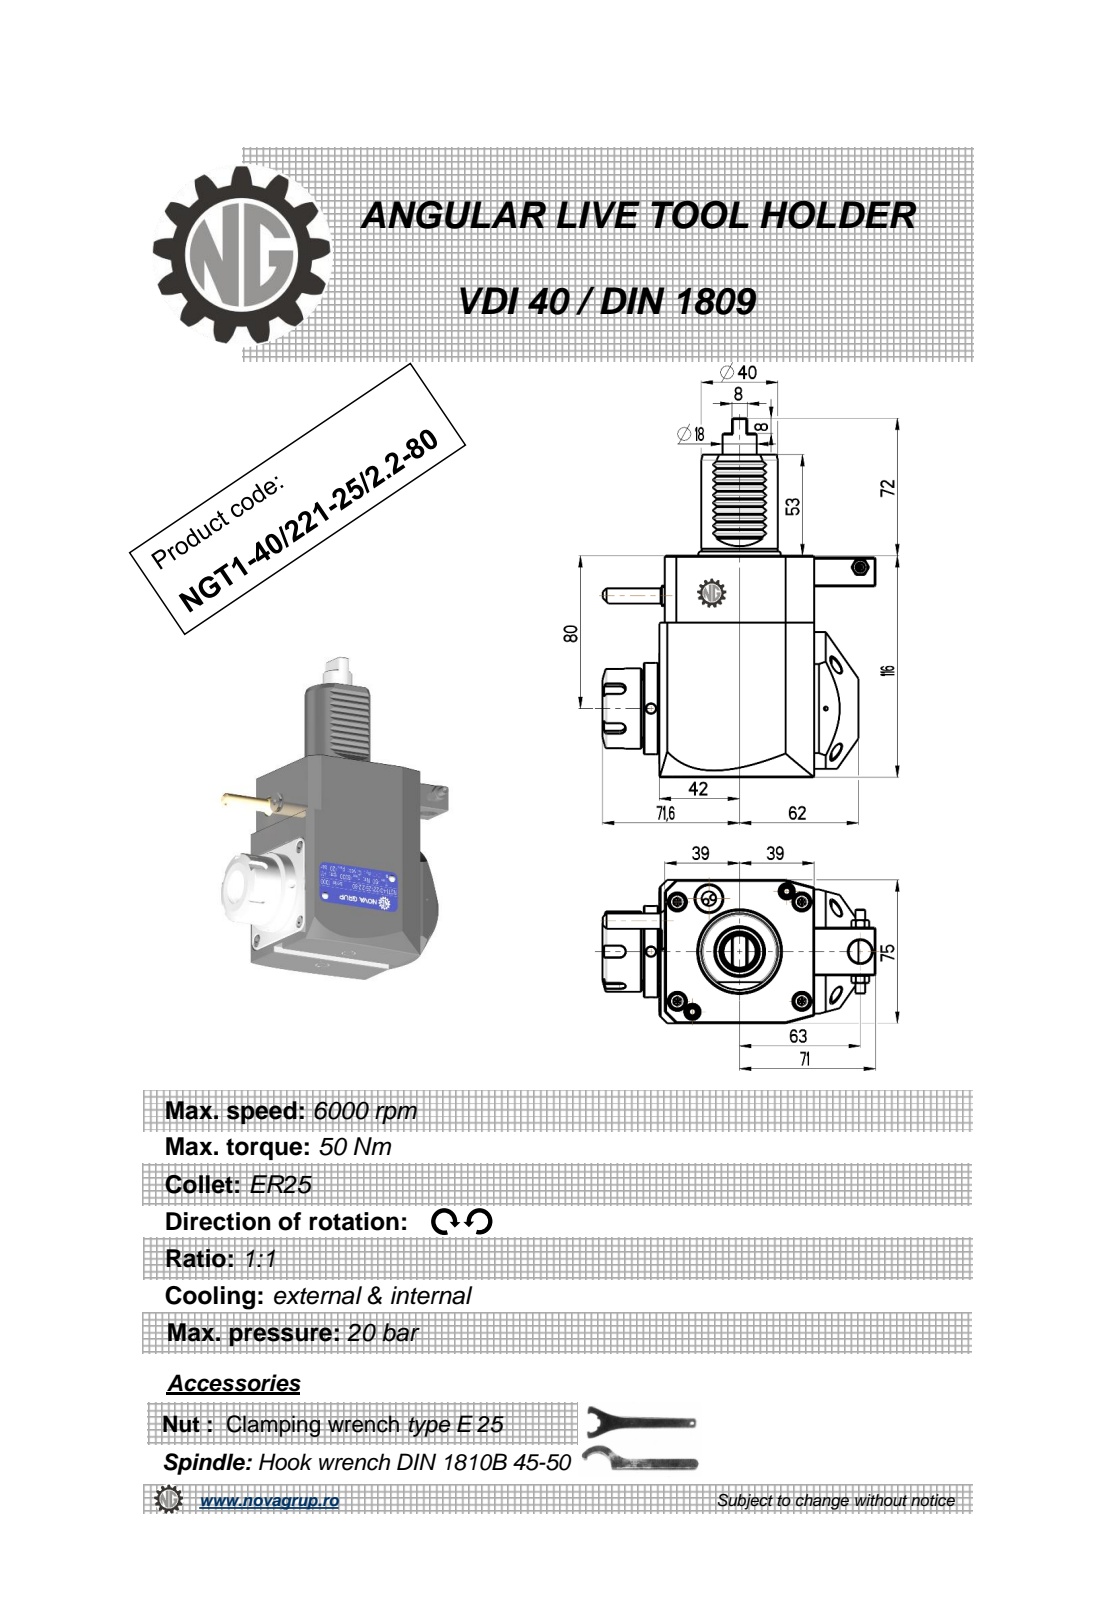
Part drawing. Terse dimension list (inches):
name: NGT1_40_221_25_2_2_80
written by: PRO/ENGINEER BY PARAMETRIC TECHNOLOGY CORPORATION, 2010280 (CONFIG_CONTROL_DESIGN)
unit: in
bodies: 1 solid, 432 faces (194 planar, 89 cylindrical, 149 other)
size: 7.402 × 5.614 × 3.016
volume: 52.89 in³; area: 108.2 in²
holes: 3× ⌀0.197, 1× ⌀0.118, 1× ⌀0.165, 1× ⌀0.374, 1× ⌀0.472, 1× ⌀0.799
bosses: 1× ⌀1.89, 1× ⌀1.654, 1× ⌀1.575, 1× ⌀1.476, 1× ⌀1.299, 1× ⌀0.701, 1× ⌀0.441, 1× ⌀0.353
rounds: 12× R0.01, 10× R0.012, 6× R0.009, 5× R0.118, 2× R0.031, 1× R0.02, 1× R1.575
face distances: 2.953, 4.567, 3.189, 0.118, 3.071, 0.11, 3.181, 4.409, 0.315, 0.984
hole spacings: 0.824, 2.407, 2.854, 4.301, 5.195
